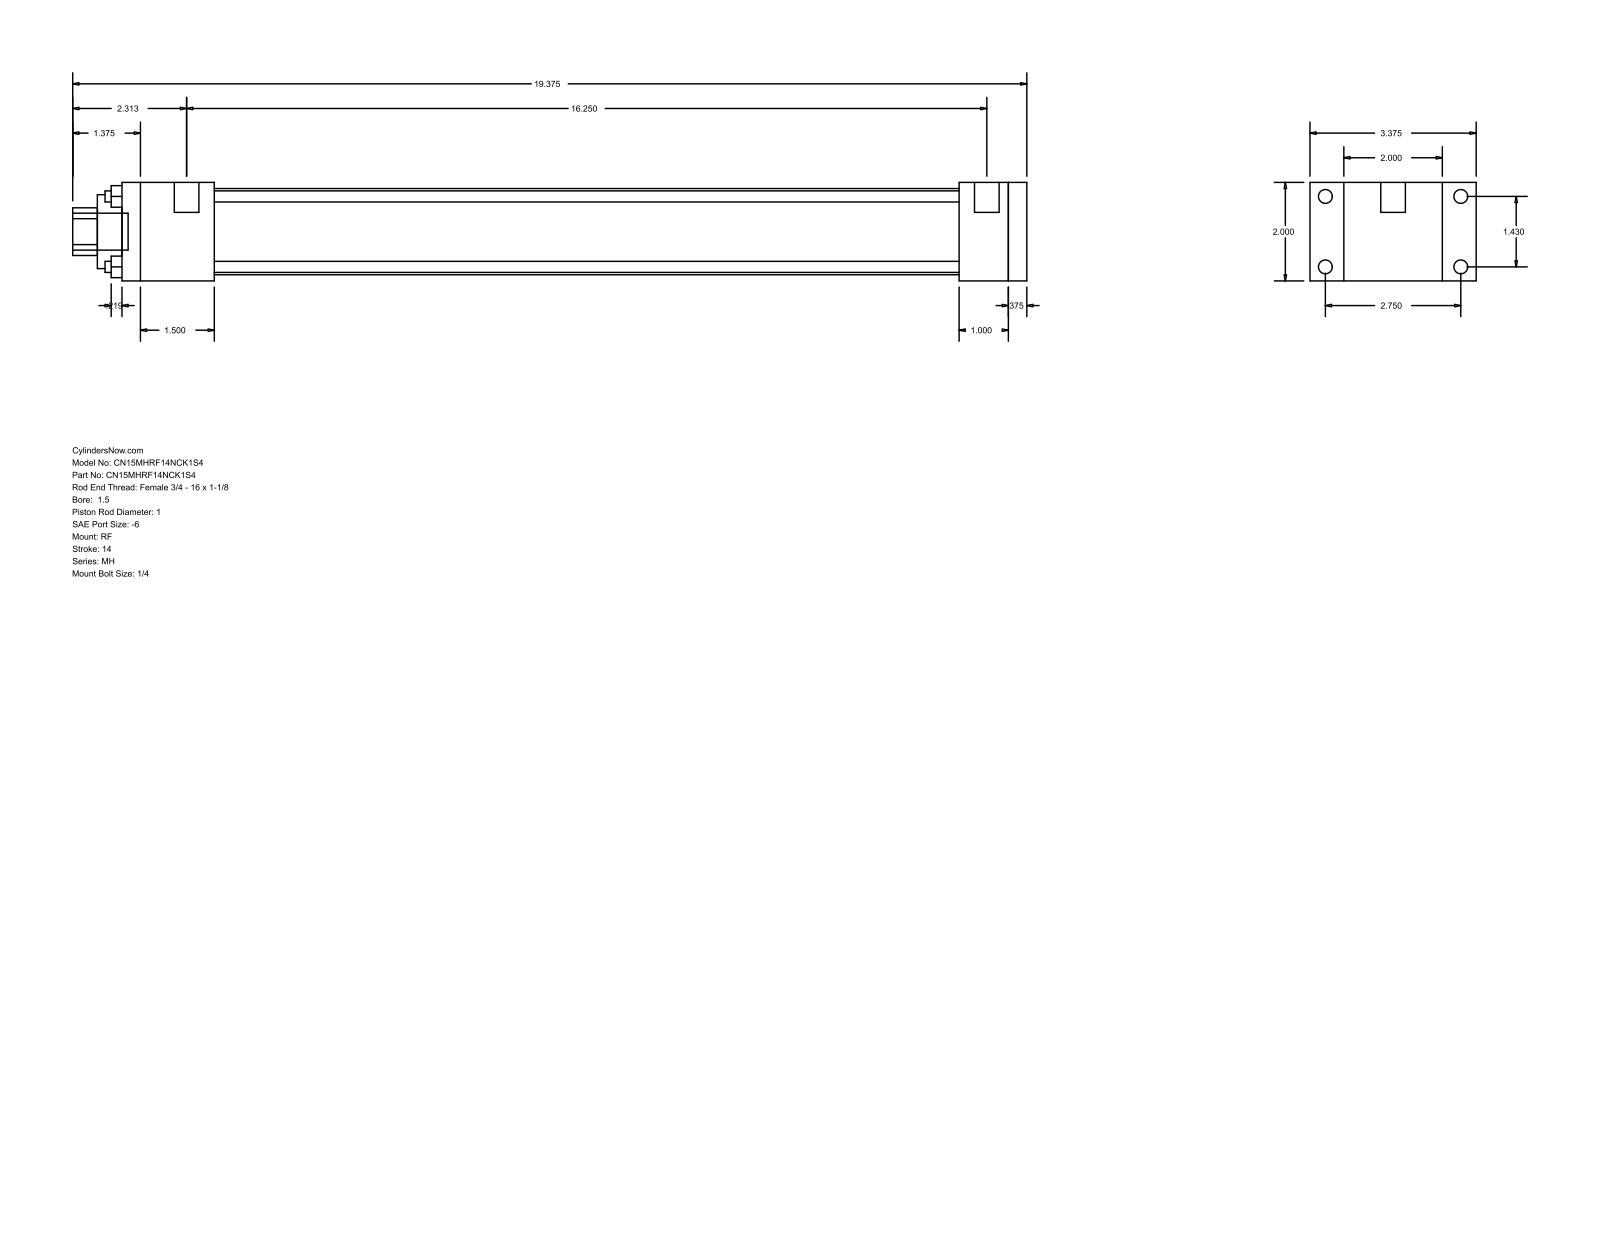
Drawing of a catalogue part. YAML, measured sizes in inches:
part_name: "MH_RF__0150_1"
step_written_by: "GSSL Pune (CONFIG_CONTROL_DESIGN)"
units: inches
bodies: {solids: 0, faces: 92, planar: 64, cylindrical: 28, other: 0}
overall_size: [19.375, 3.375, 2]
round_holes:
  - {diameter: 0.225, count: 4}
  - {diameter: 1, count: 1}
  - {diameter: 1.5, count: 1}
  - {diameter: 1.75, count: 1}
round_bosses_or_shafts:
  - {diameter: 0.281, count: 4}
  - {diameter: 0.219, count: 4}
  - {diameter: 0.5, count: 2}
  - {diameter: 0.75, count: 1}
partial_cylinders:
  - {radius: 0.484, count: 1}
face_to_face_distances: [2, 0.375, 18, 1, 18.375, 0.687, 2.687, 17, 1.375, 1.875]
hole_center_spacings: [1.011, 1.43, 2.022]
